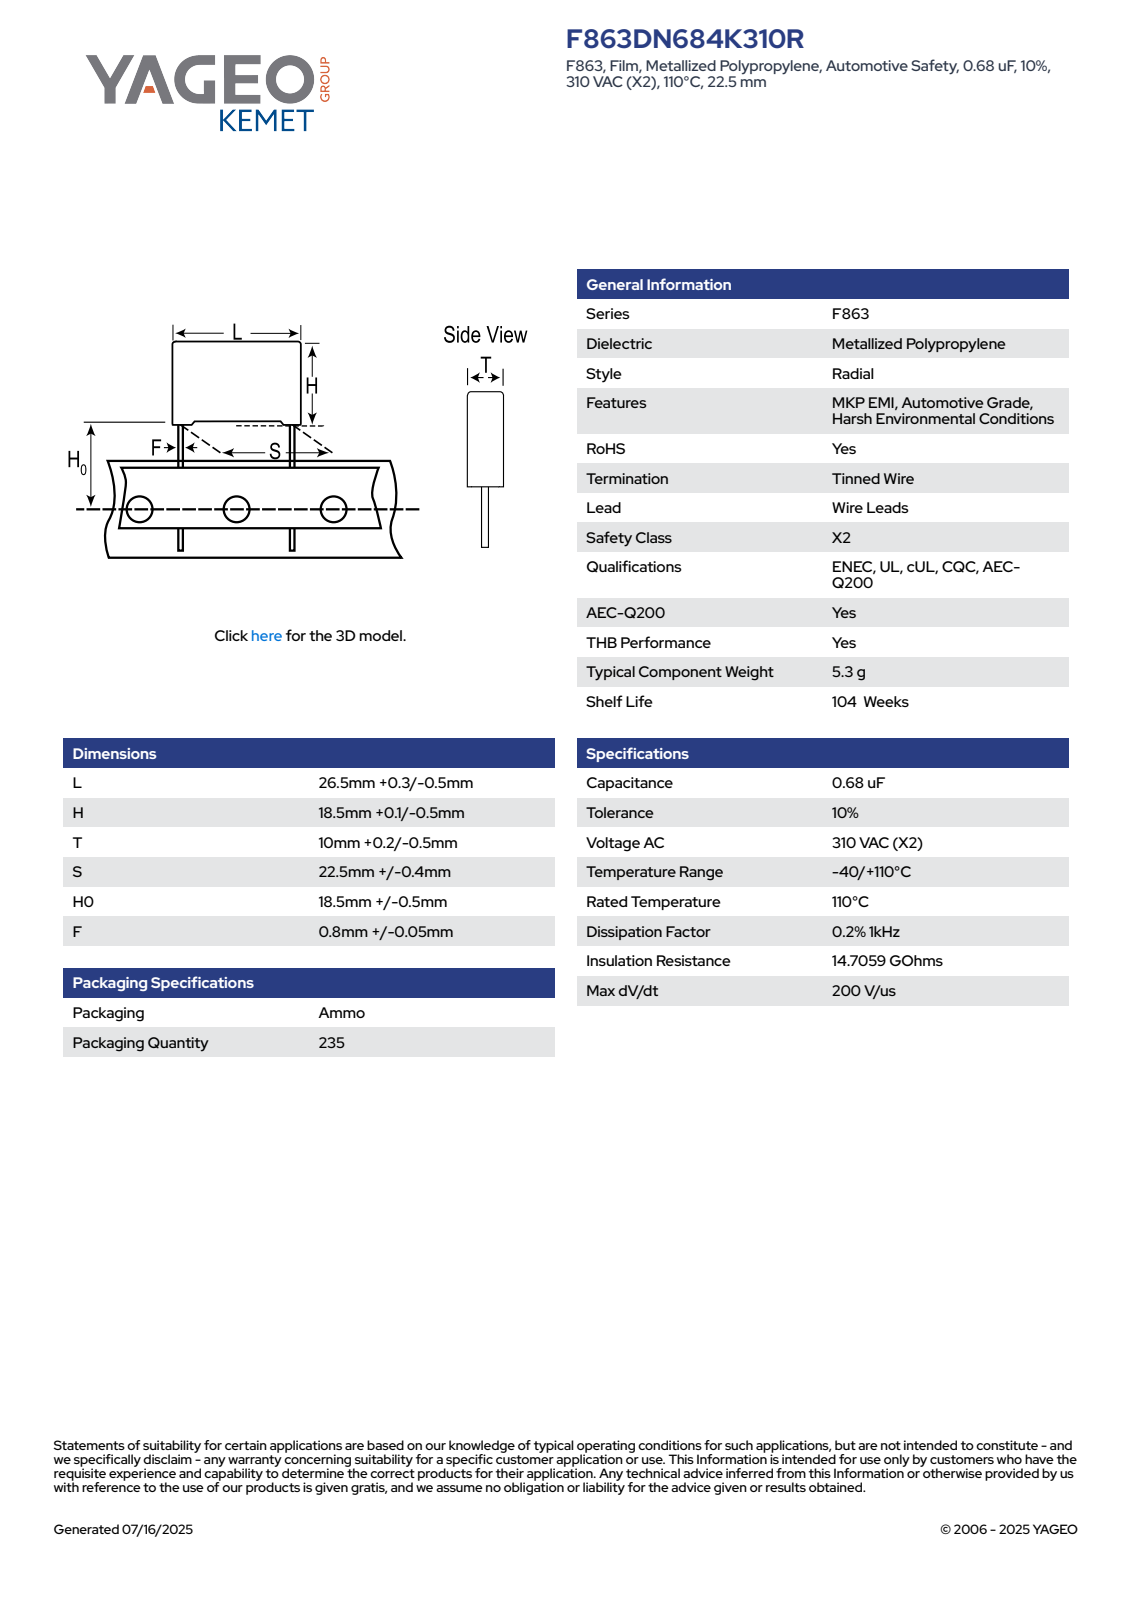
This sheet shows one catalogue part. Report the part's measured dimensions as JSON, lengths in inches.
{"part_name": "CFR_RB2_26.5X18.5X10_L26.8H18.6T10.2S22.5H019F0.85", "step_written_by": "SolidWorks 2020 (AUTOMOTIVE_DESIGN)", "units": "inches", "bodies": {"solids": 4, "faces": 85, "planar": 77, "cylindrical": 8, "other": 0}, "overall_size": [1.48, 1.055, 0.402], "volume_in3": 0.3, "surface_area_in2": 3.207, "round_bosses_or_shafts": [[0.033, 2]], "partial_cylinders_radius": [[0.02, 4]], "face_to_face_distances": [0.402, 0.703, 1.055, 0.707, 0.03, 0.025, 0.732, 0.035, 0.367, 1.02]}
